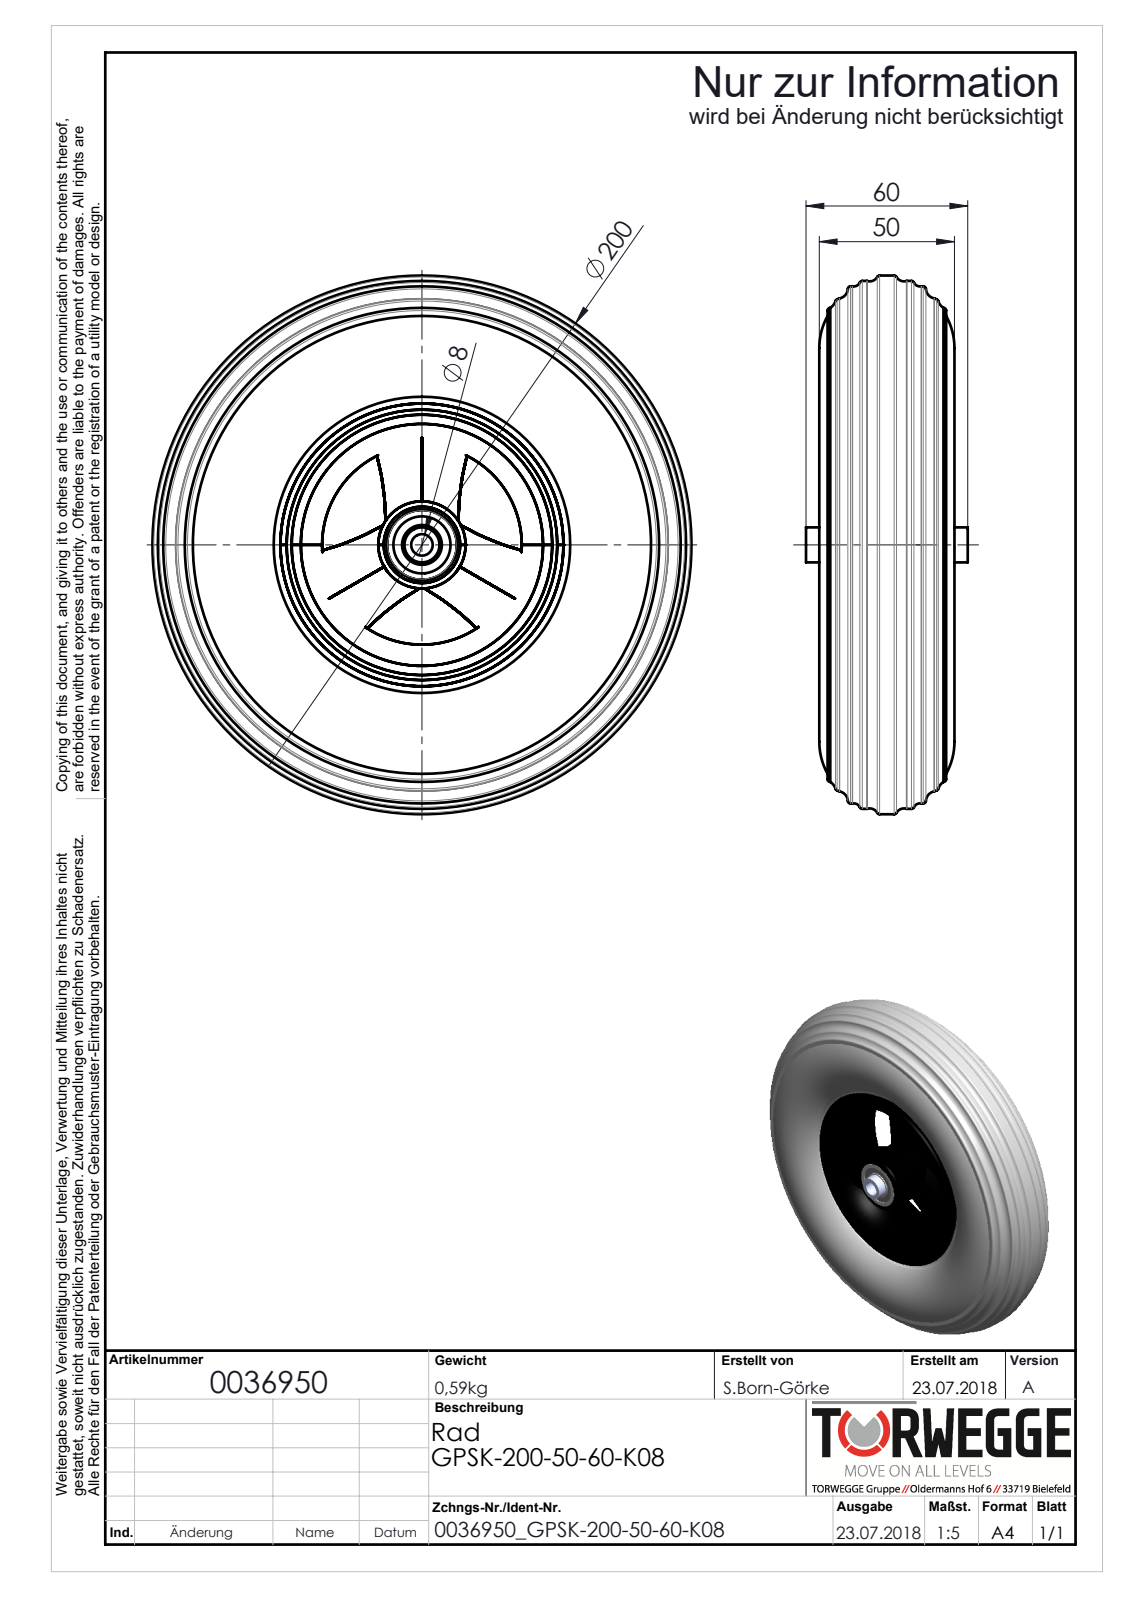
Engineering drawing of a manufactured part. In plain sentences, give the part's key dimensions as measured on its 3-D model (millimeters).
The part is named "0036950_GPSK-200-50-60-K08". Its 3-D file was written by "SolidWorks 2016 (AUTOMOTIVE_DESIGN)". It is 0 solids with 196 faces: 16 planar, 32 cylindrical and 148 other. Overall it measures 200 by 200 by 61.2 millimeters. Round holes: 1 of diameter 8, 1 of diameter 21.2. Round bosses or shafts: 1 of diameter 200, 1 of diameter 196, 1 of diameter 192, 1 of diameter 105, 1 of diameter 32.4, 1 of diameter 14.8, 1 of diameter 13. The main face-to-face distances are 7.1, 36.9, 2.5, 44, 41.5, 4.6, 34.4, 29.8, 3, 5.5.
